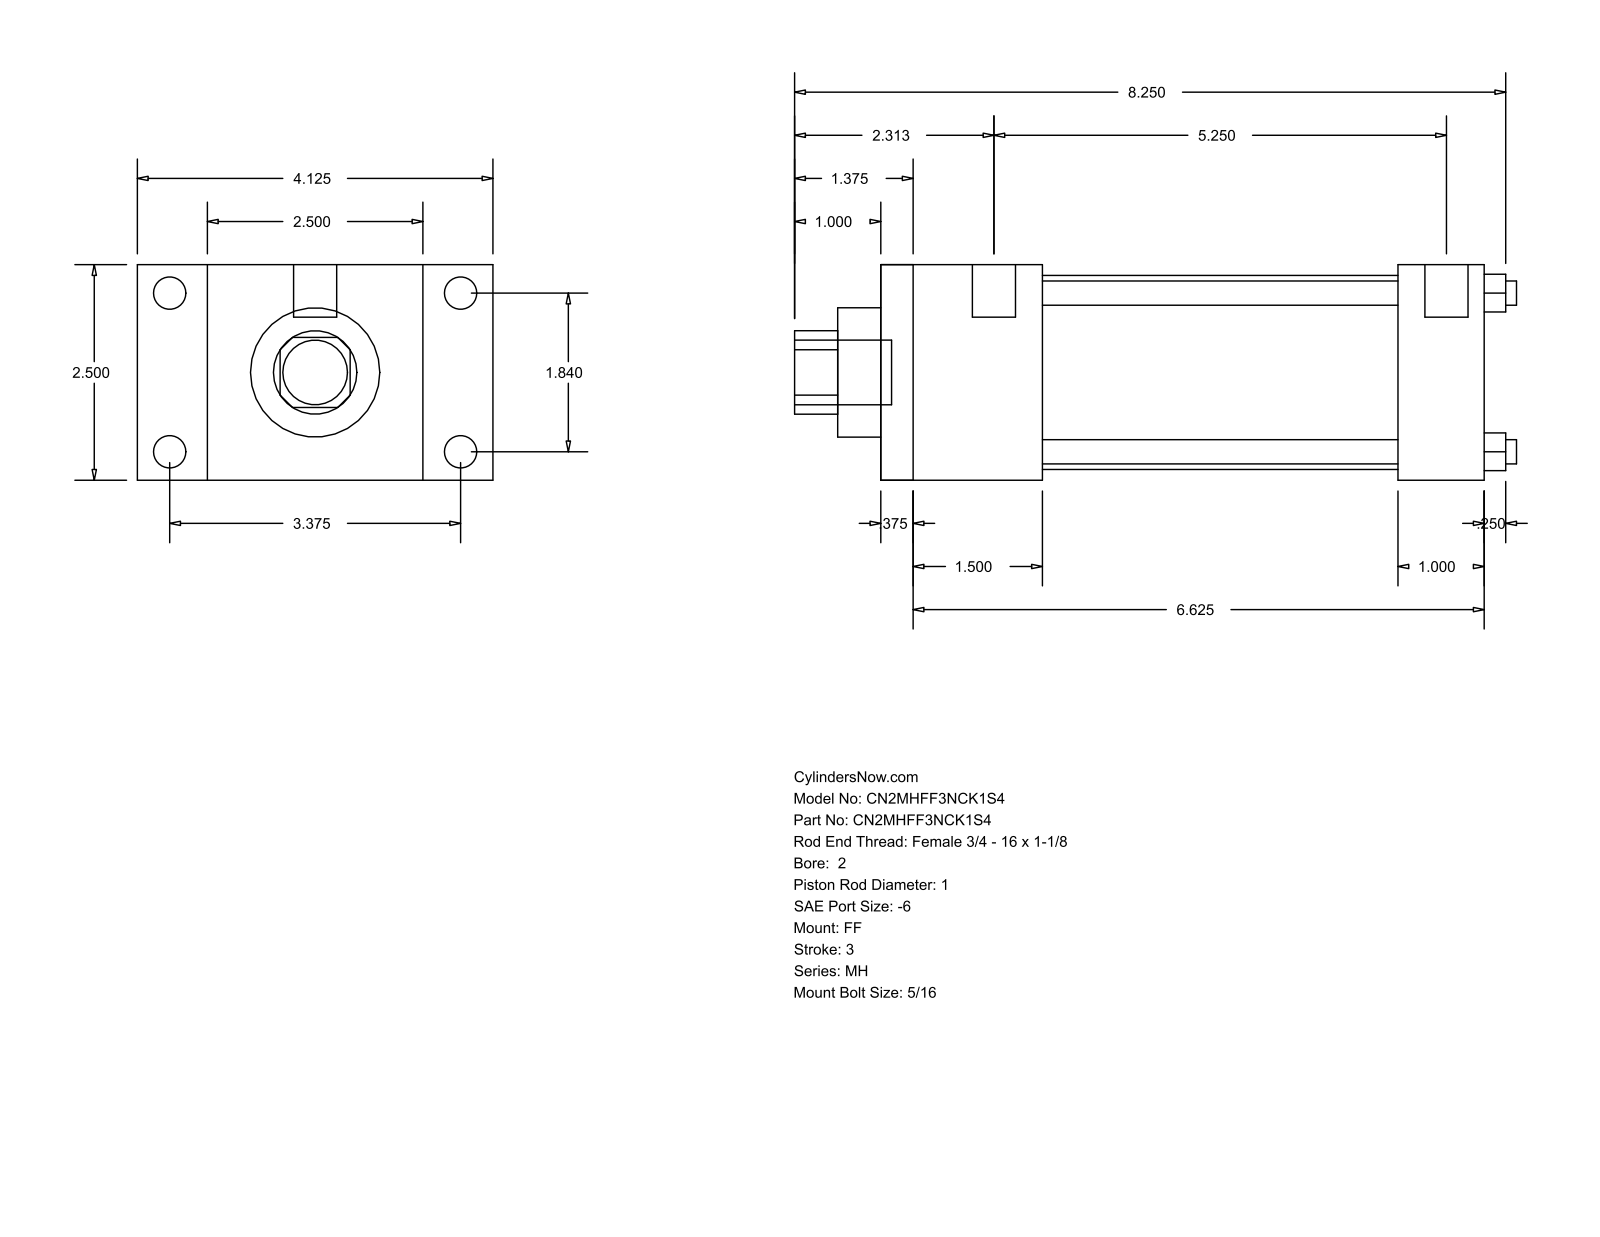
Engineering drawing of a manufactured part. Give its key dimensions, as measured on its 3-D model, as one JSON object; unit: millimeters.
{"part_name": "MH_FF__0200_1", "step_written_by": "GSSL Pune (CONFIG_CONTROL_DESIGN)", "units": "millimeters", "bodies": {"solids": 0, "faces": 92, "planar": 64, "cylindrical": 28, "other": 0}, "overall_size": [212.72, 104.78, 63.5], "round_holes": [[7.14, 4], [25.4, 1], [38.1, 1], [57.15, 1]], "round_bosses_or_shafts": [[9.53, 4], [5.56, 4], [12.7, 2], [19.05, 1]], "partial_cylinders_radius": [[12.29, 1]], "face_to_face_distances": [63.5, 177.8, 9.52, 168.28, 20.64, 25.4, 47.63, 152.4, 38.11, 142.88], "hole_center_spacings": [33.05, 46.74, 66.1]}
